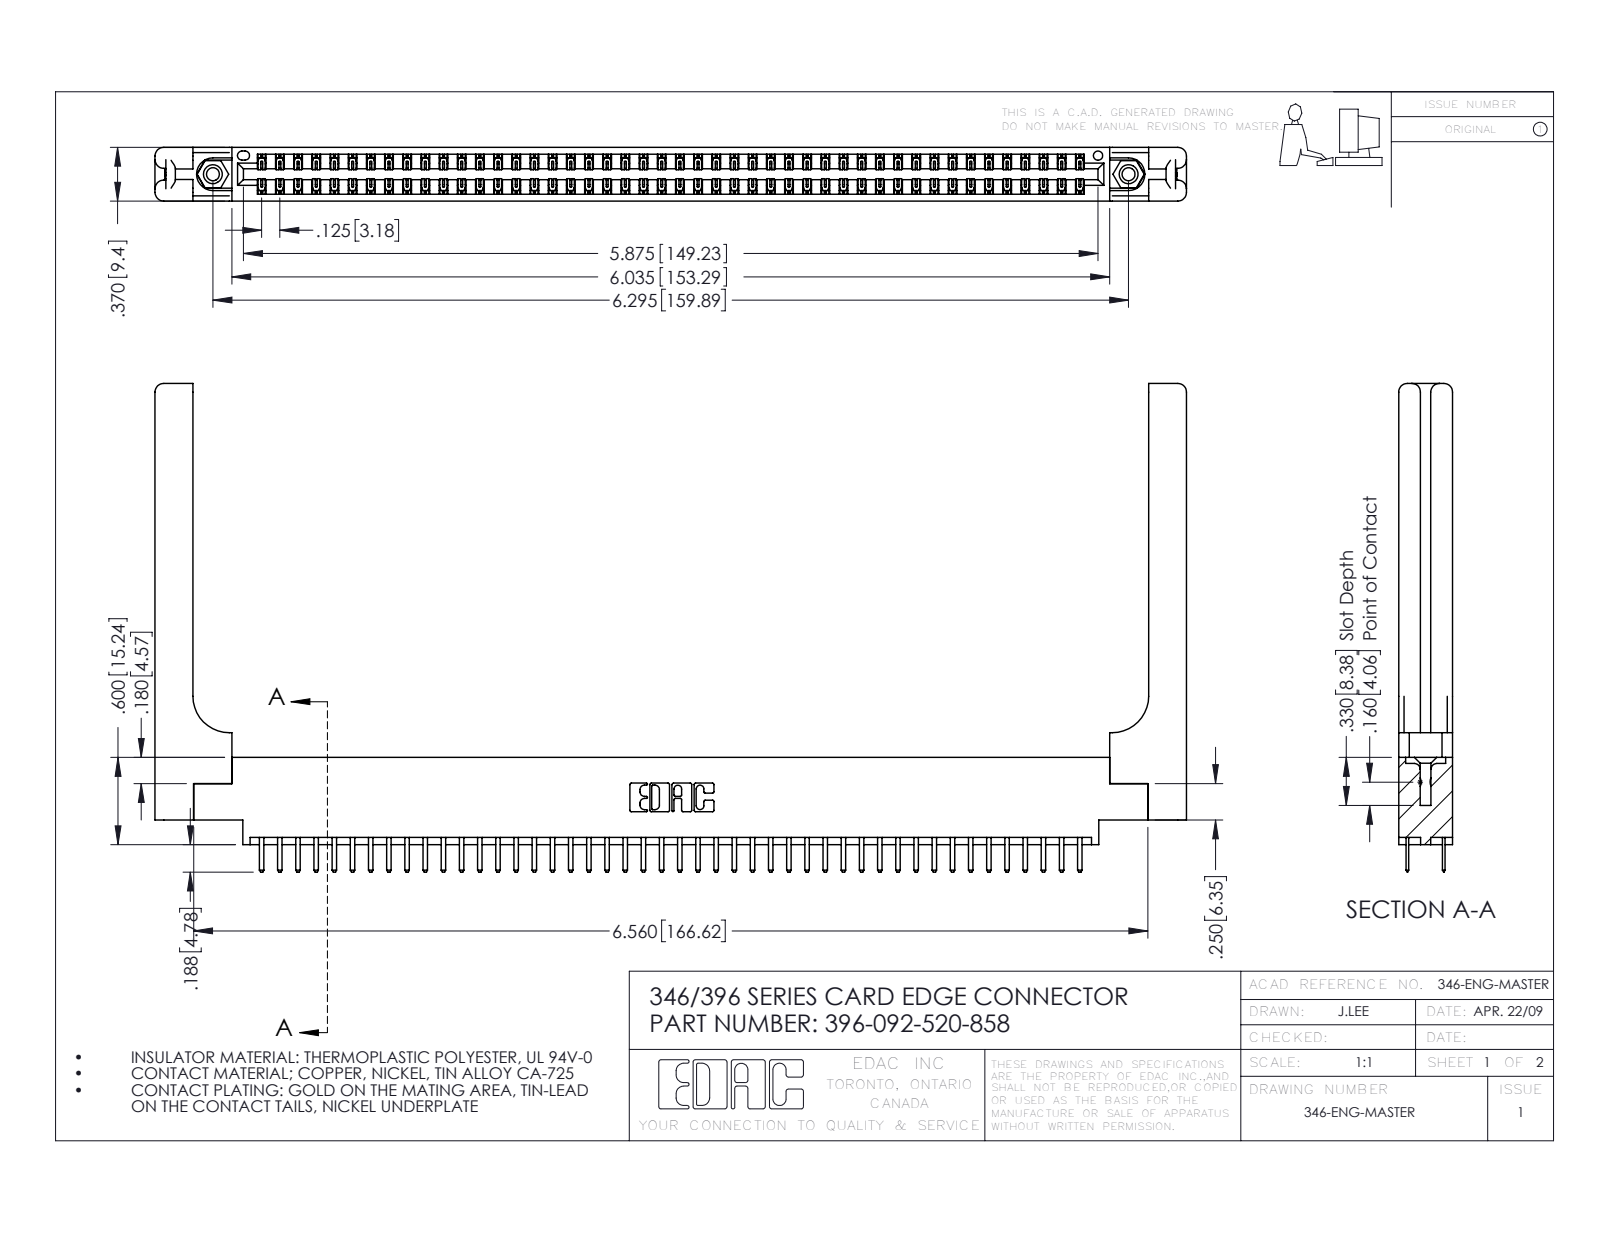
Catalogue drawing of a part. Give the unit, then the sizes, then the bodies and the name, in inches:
Units: inches
Overall size (bounding box): 7.091 × 3.358 × 0.37
Round holes (diameter × count): ⌀0.089 ×2, ⌀0.125 ×2, ⌀0.156 ×2, ⌀0.064 ×1
Round bosses / shafts (diameter × count): ⌀0.155 ×2
Partial cylindrical surfaces — rounded edges, fillets, slot ends (radius × count): R0.006 ×138, R0.01 ×96, R0.01 ×22, R0.06 ×16, R0.007 ×6, R0.031 ×6, R0.026 ×3, R0.014 ×2
Main face-to-face distances: 0.37, 0.048, 0.322, 0.072, 0.25, 0.148, 0.15, 0.298, 0.025, 0.275
Hole centre spacings: 0.246, 6.086, 6.295
Volume: 1.519 in³ · Surface area: 45.01 in²
Bodies: 97 solids, 5534 faces (3632 planar, 1842 cylindrical, 60 other)
Part name (STEP PRODUCT): 396-092-520-858; 346-220-058_345-220-058; 345-250-001_345-250-001-102; 346 Part_0.170 Offset - 0.156 Dia-TH (+1 more)
STEP written by: SolidWorks 2016 (CONFIG_CONTROL_DESIGN)
